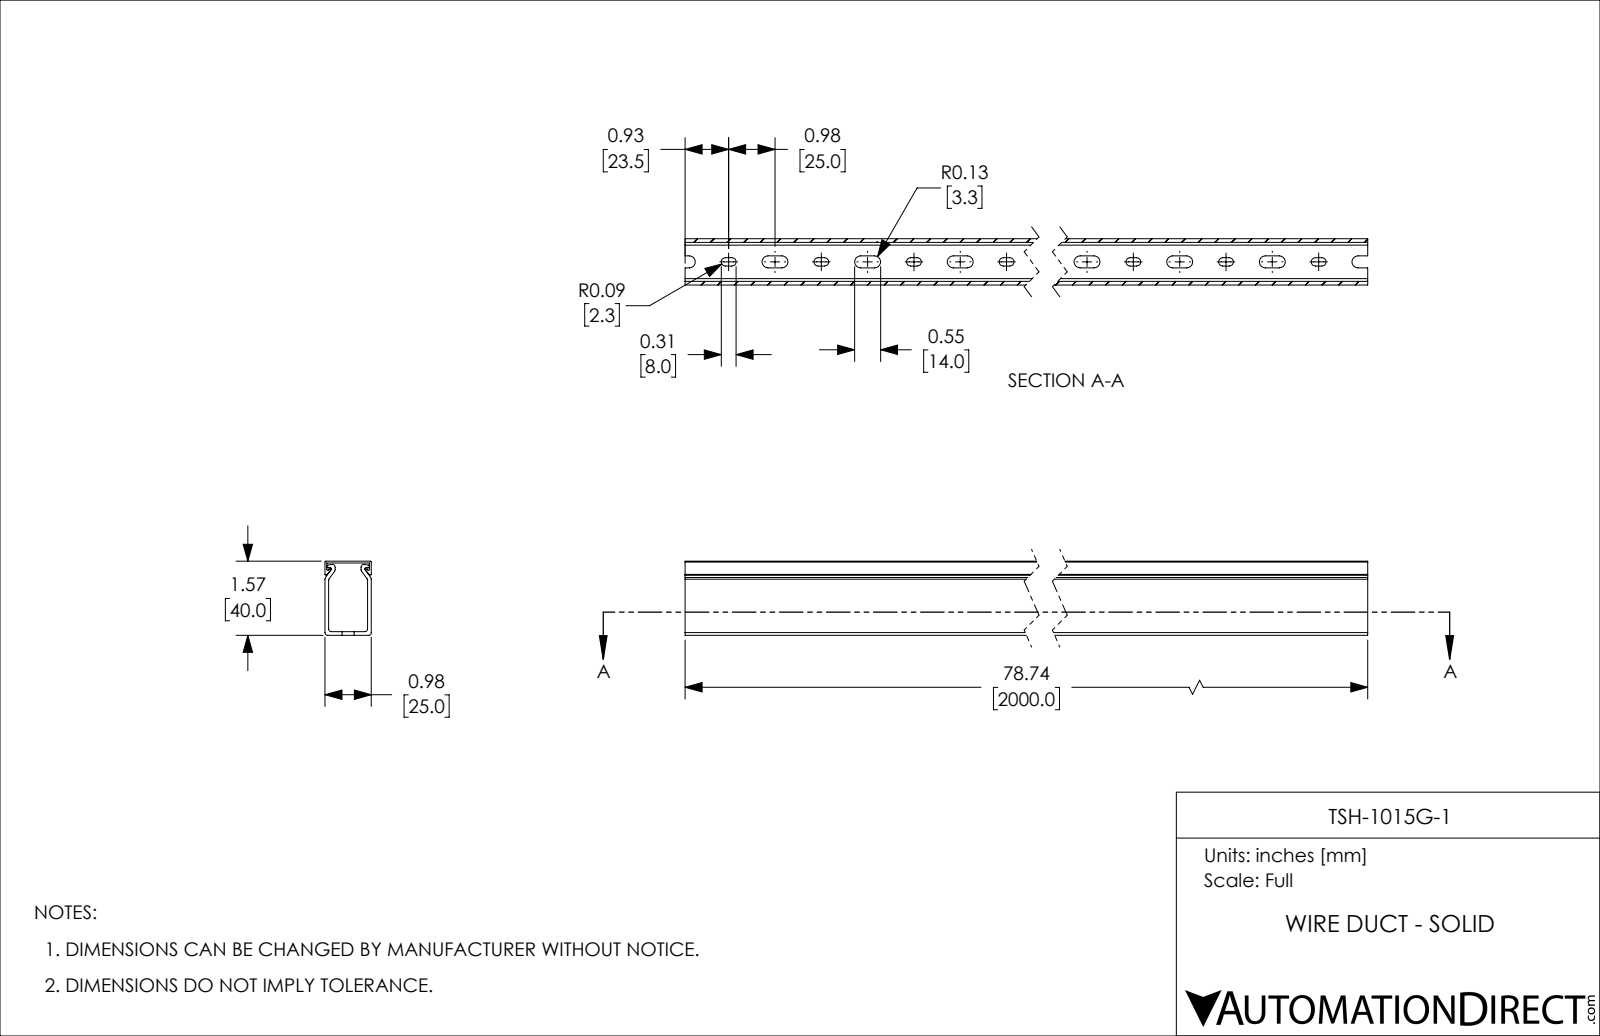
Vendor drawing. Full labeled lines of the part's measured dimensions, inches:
Part name (STEP PRODUCT): TSH-1015G-1
STEP written by: SolidWorks 2021 (CONFIG_CONTROL_DESIGN)
Units: inches
Bodies: 2 solids, 465 faces (194 planar, 271 cylindrical, 0 other)
Overall size (bounding box): 78.74 × 1.575 × 0.984
Volume: 30 in³ · Surface area: 897.5 in²
Partial cylindrical surfaces — rounded edges, fillets, slot ends (radius × count): R0.089 ×80, R0.128 ×80, R0.059 ×12, R0.02 ×8, R0.03 ×6
Main face-to-face distances: 0.079, 0.906, 0.039, 0.984, 0.827, 1.535, 1.575, 1.457, 1.496, 0.945
